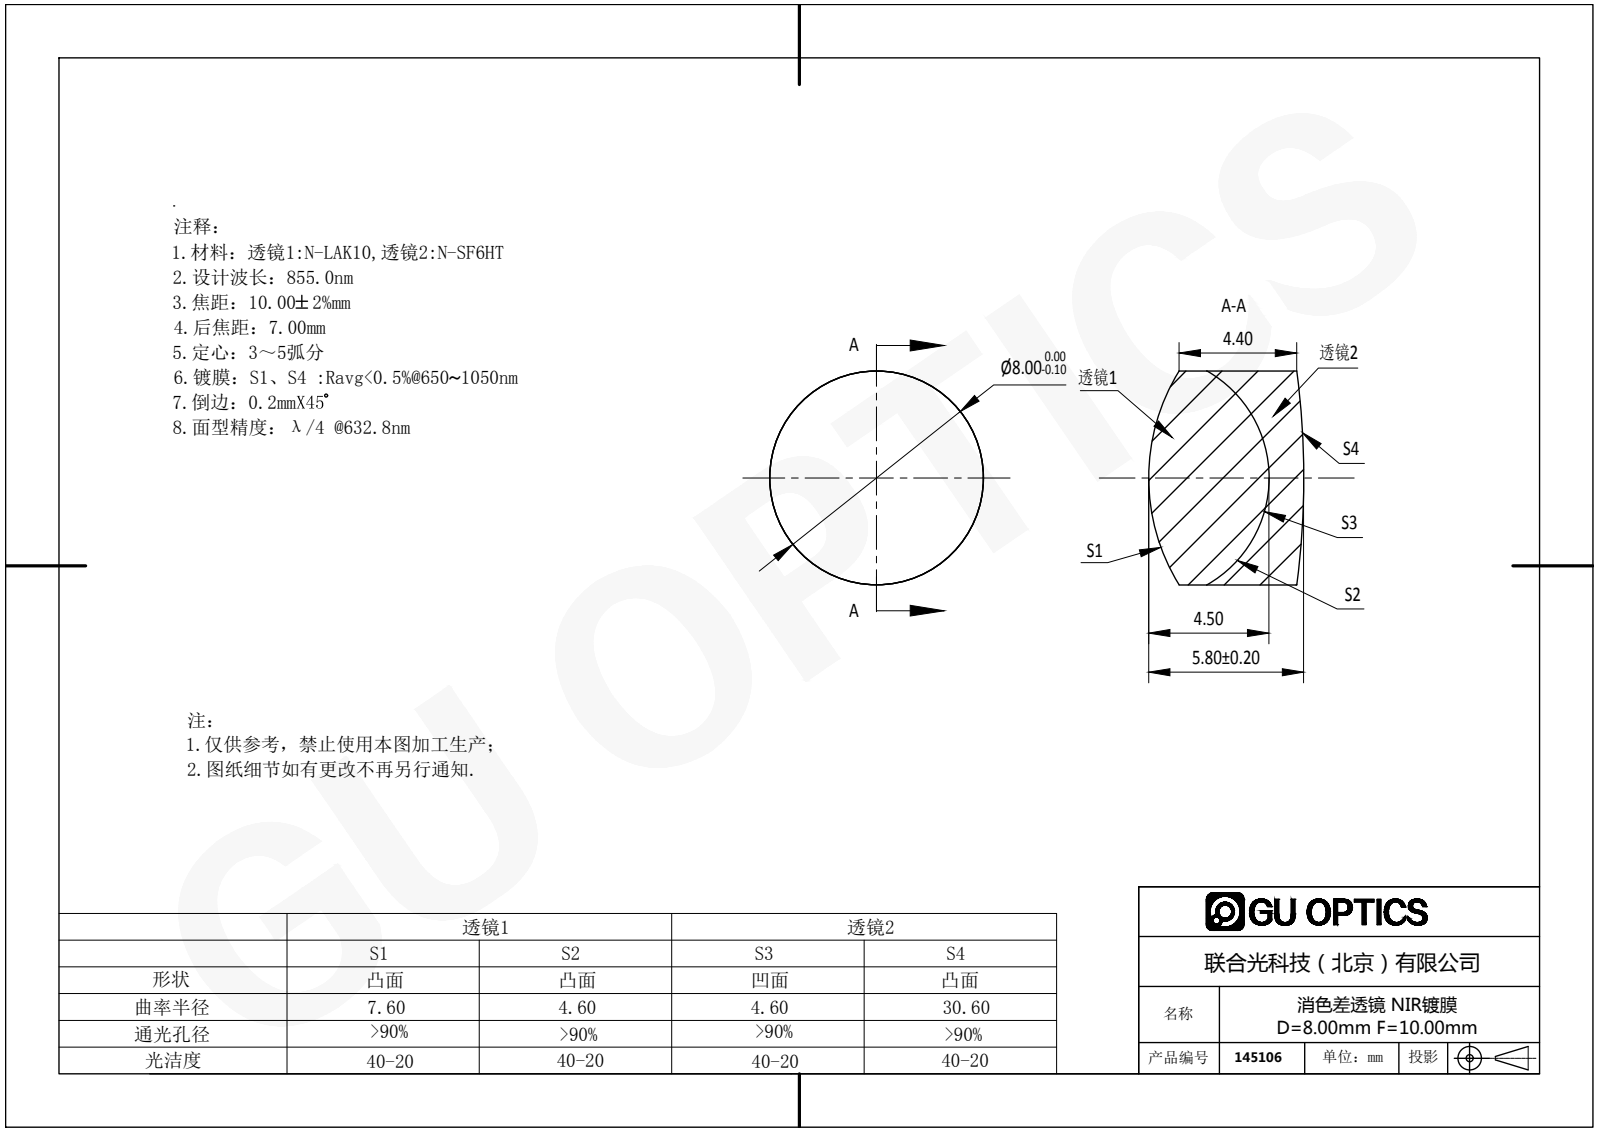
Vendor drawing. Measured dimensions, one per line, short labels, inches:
name: 145106
written by: SolidWorks 2016 (AUTOMOTIVE_DESIGN)
unit: in
bodies: 2 solids, 12 faces (0 planar, 4 cylindrical, 8 other)
size: 0.315 × 0.315 × 0.228
volume: 0.016 in³; area: 0.543 in²
bosses: 1× ⌀0.315
